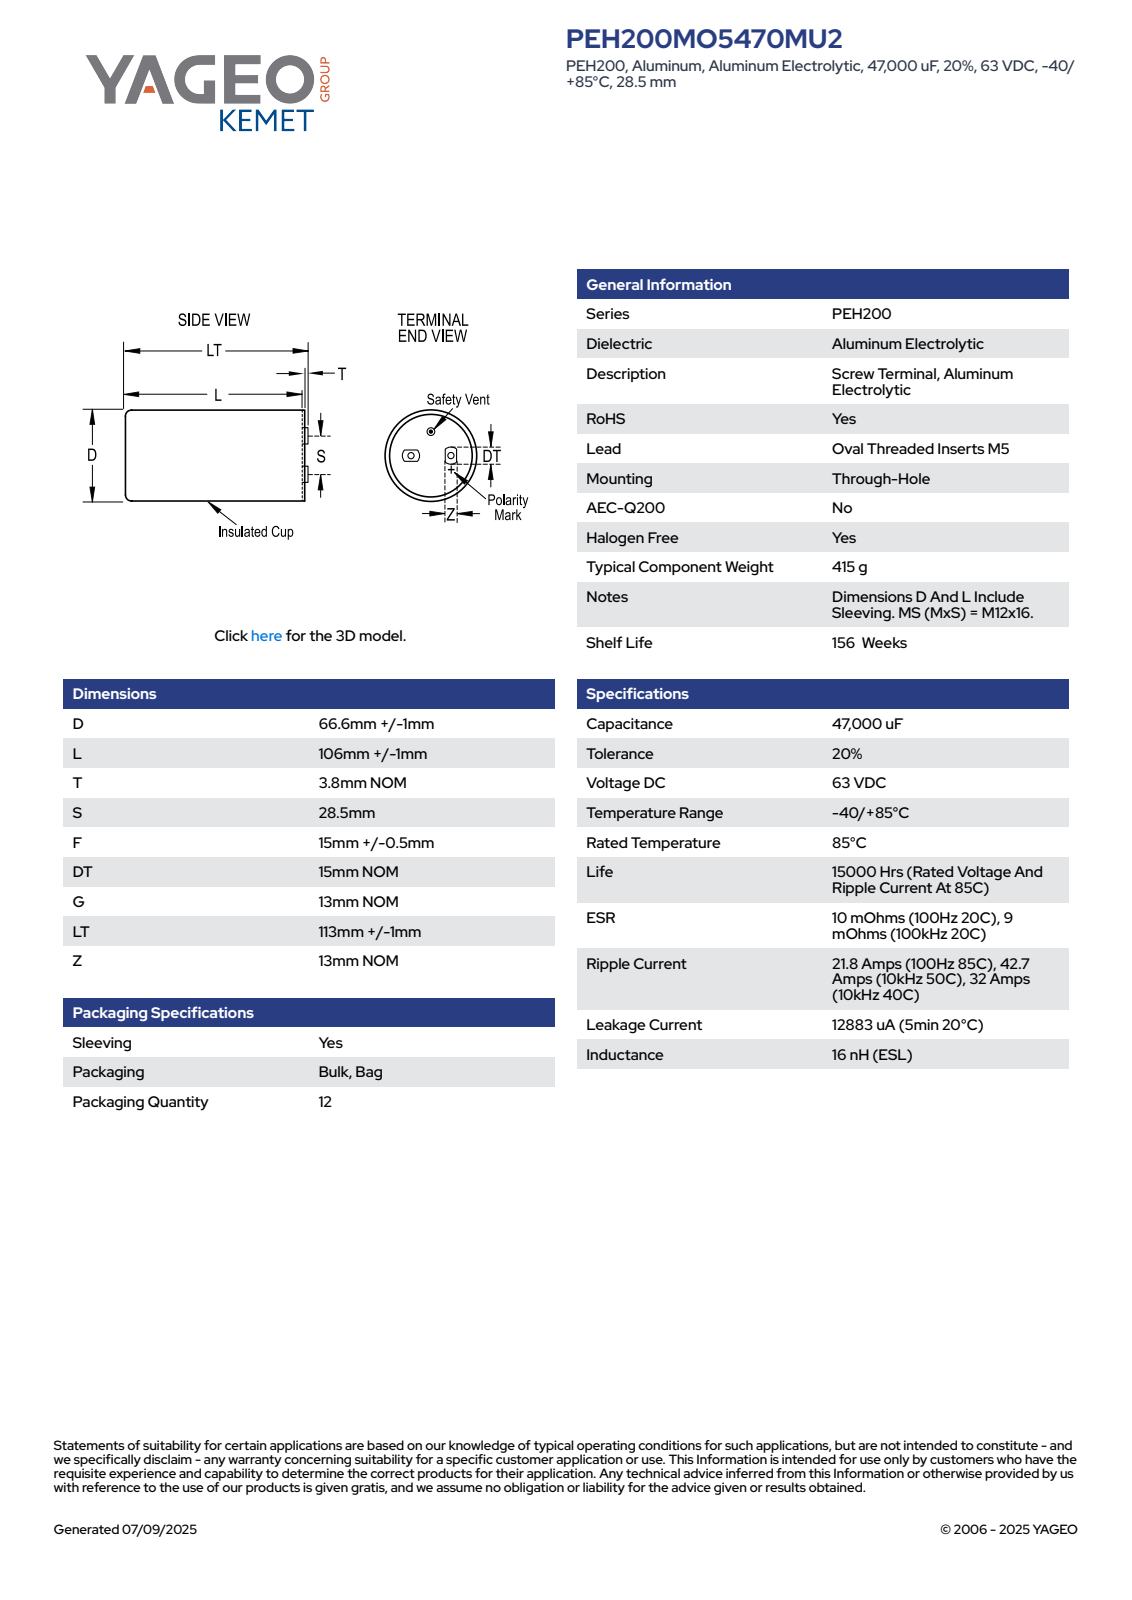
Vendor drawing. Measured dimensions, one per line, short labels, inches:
name: Oval_Terminal_4; CARC_D67.6L107S28.5T3.8; Can_4
written by: SolidWorks 2014 (AUTOMOTIVE_DESIGN)
unit: in
bodies: 3 solids, 91 faces (38 planar, 21 cylindrical, 32 other)
size: 4.488 × 2.661 × 2.661
volume: 23.59 in³; area: 50.61 in²
holes: 2× ⌀0.158, 1× ⌀2.583
bosses: 2× ⌀0.295, 1× ⌀2.661
rounds: 2× R0.295, 1× R1.33
face distances: 4.213, 0.276, 4.488, 0.15, 0.126, 4.339, 0.512, 0.197, 0.472, 0.323
hole spacings: 0.561, 1.122
